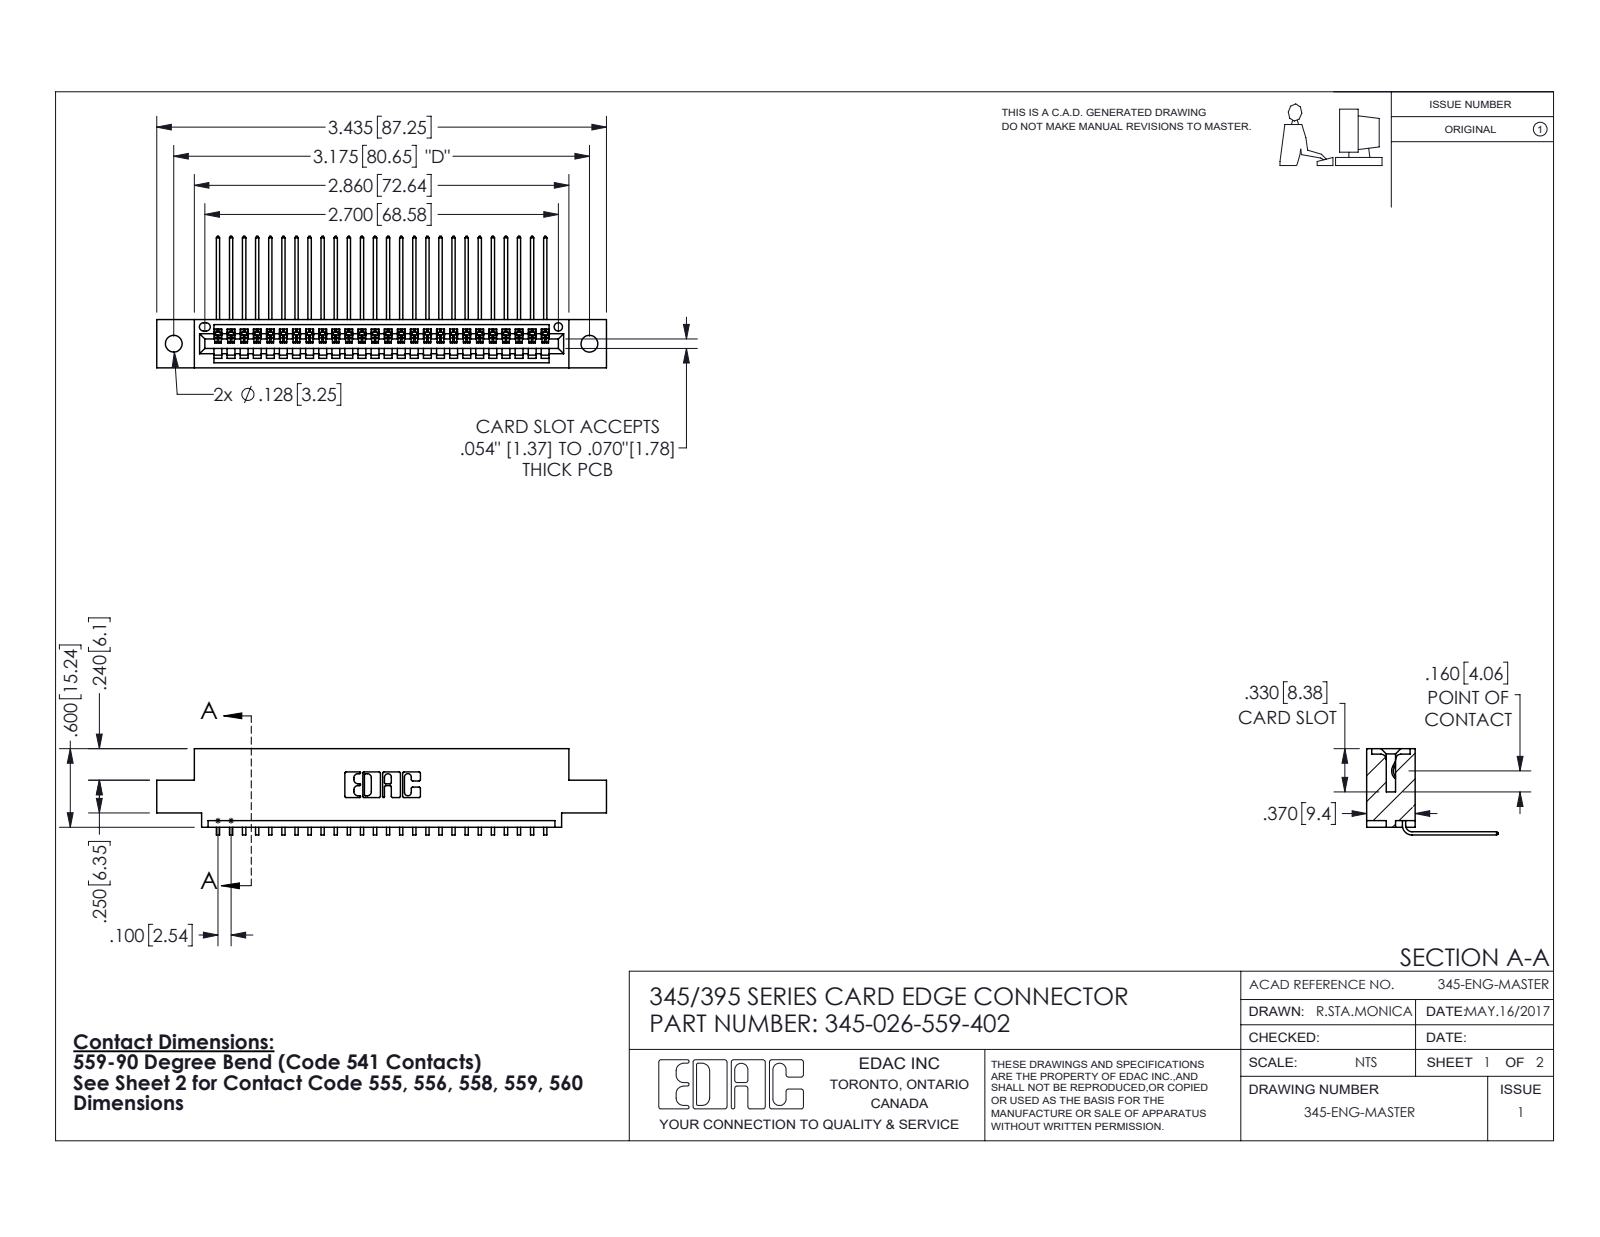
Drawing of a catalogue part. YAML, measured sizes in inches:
part_name: "345-026-559-402; 345 Part_0.110 Offset - 0.128 Dia; 345-292-001_558 559 Tail - 1"
step_written_by: "SolidWorks 2016 (CONFIG_CONTROL_DESIGN)"
units: inches
bodies: {solids: 27, faces: 1690, planar: 1176, cylindrical: 514, other: 0}
overall_size: [3.435, 1.005, 0.659]
volume: 0.496
surface_area: 16.91
round_holes:
  - {diameter: 0.128, count: 2}
  - {diameter: 0.064, count: 1}
partial_cylinders:
  - {radius: 0.006, count: 52}
  - {radius: 0.01, count: 22}
  - {radius: 0.007, count: 6}
  - {radius: 0.031, count: 6}
  - {radius: 0.026, count: 3}
  - {radius: 0.031, count: 2}
  - {radius: 0.04, count: 2}
  - {radius: 0.014, count: 1}
face_to_face_distances: [0.072, 0.298, 0.37, 0.2, 0.098, 0.272, 0.025, 0.225, 0.149, 0.072]
hole_center_spacings: [0.27, 2.94, 3.175]
